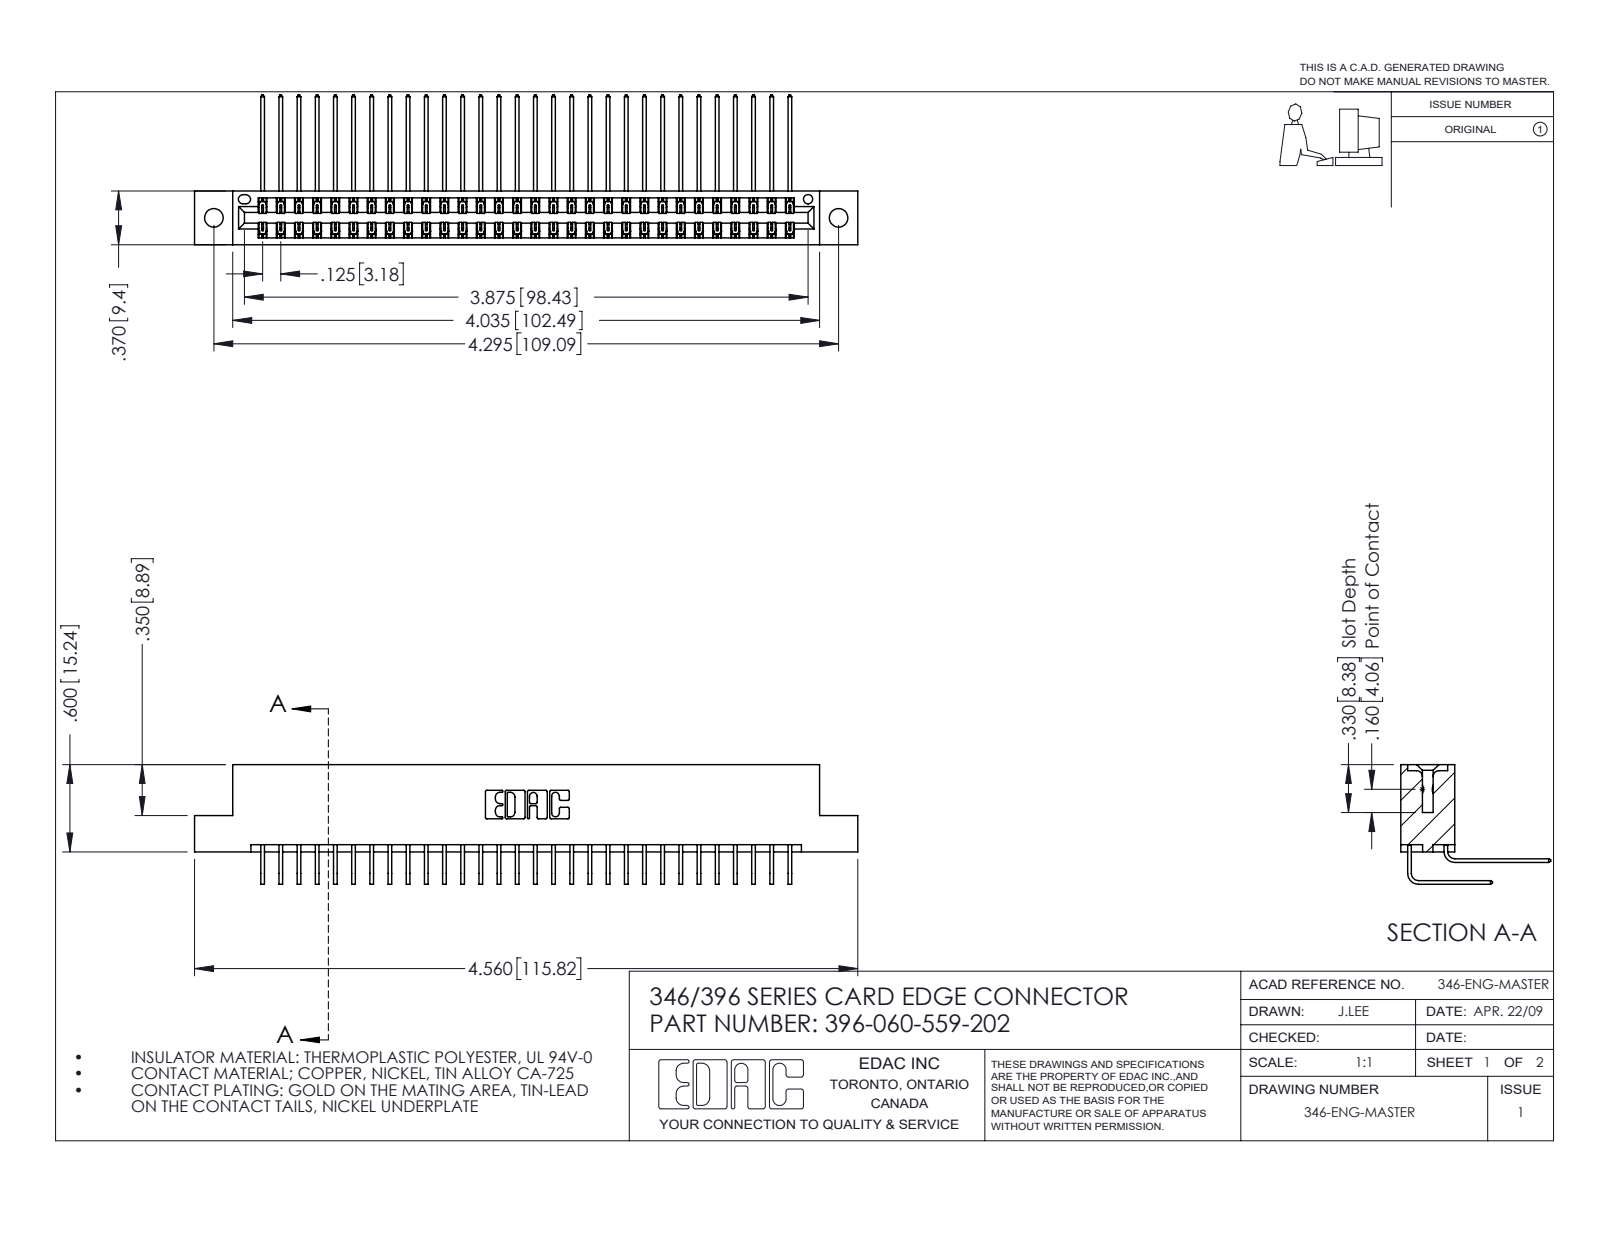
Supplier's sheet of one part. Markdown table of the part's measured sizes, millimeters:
| quantity | value |
| --- | --- |
| part name | 396-060-559-202; 345-292-001_558 559 Tail - 1; 345-292-001_559 Tail - 2; 346 Part_Flush Mounting Lugs - 0.128 Dia |
| STEP written by | SolidWorks 2016 (CONFIG_CONTROL_DESIGN) |
| units | millimeters |
| bodies | 61 solids, 3362 faces (2296 planar, 1066 cylindrical, 0 other) |
| overall size | 115.8 × 26.2 × 20.9 |
| volume | 11 500 mm³ |
| surface area | 17 030 mm² |
| round holes (diameter × count) | 3.3 × 2, 1.6 × 1 |
| partial cylindrical surfaces (radius × count) | 0.2 × 90, 0.3 × 22, 0.2 × 6, 0.8 × 6, 0.7 × 3, 0.4 × 2, 0.6 × 2, 0.6 × 2 |
| main face-to-face distances | 1.2, 8.2, 0.6, 6.4, 9.4, 1.8, 7.6, 7, 3.8, 5.6 |
| hole center spacings | 6.2, 103.8, 109.1 |
